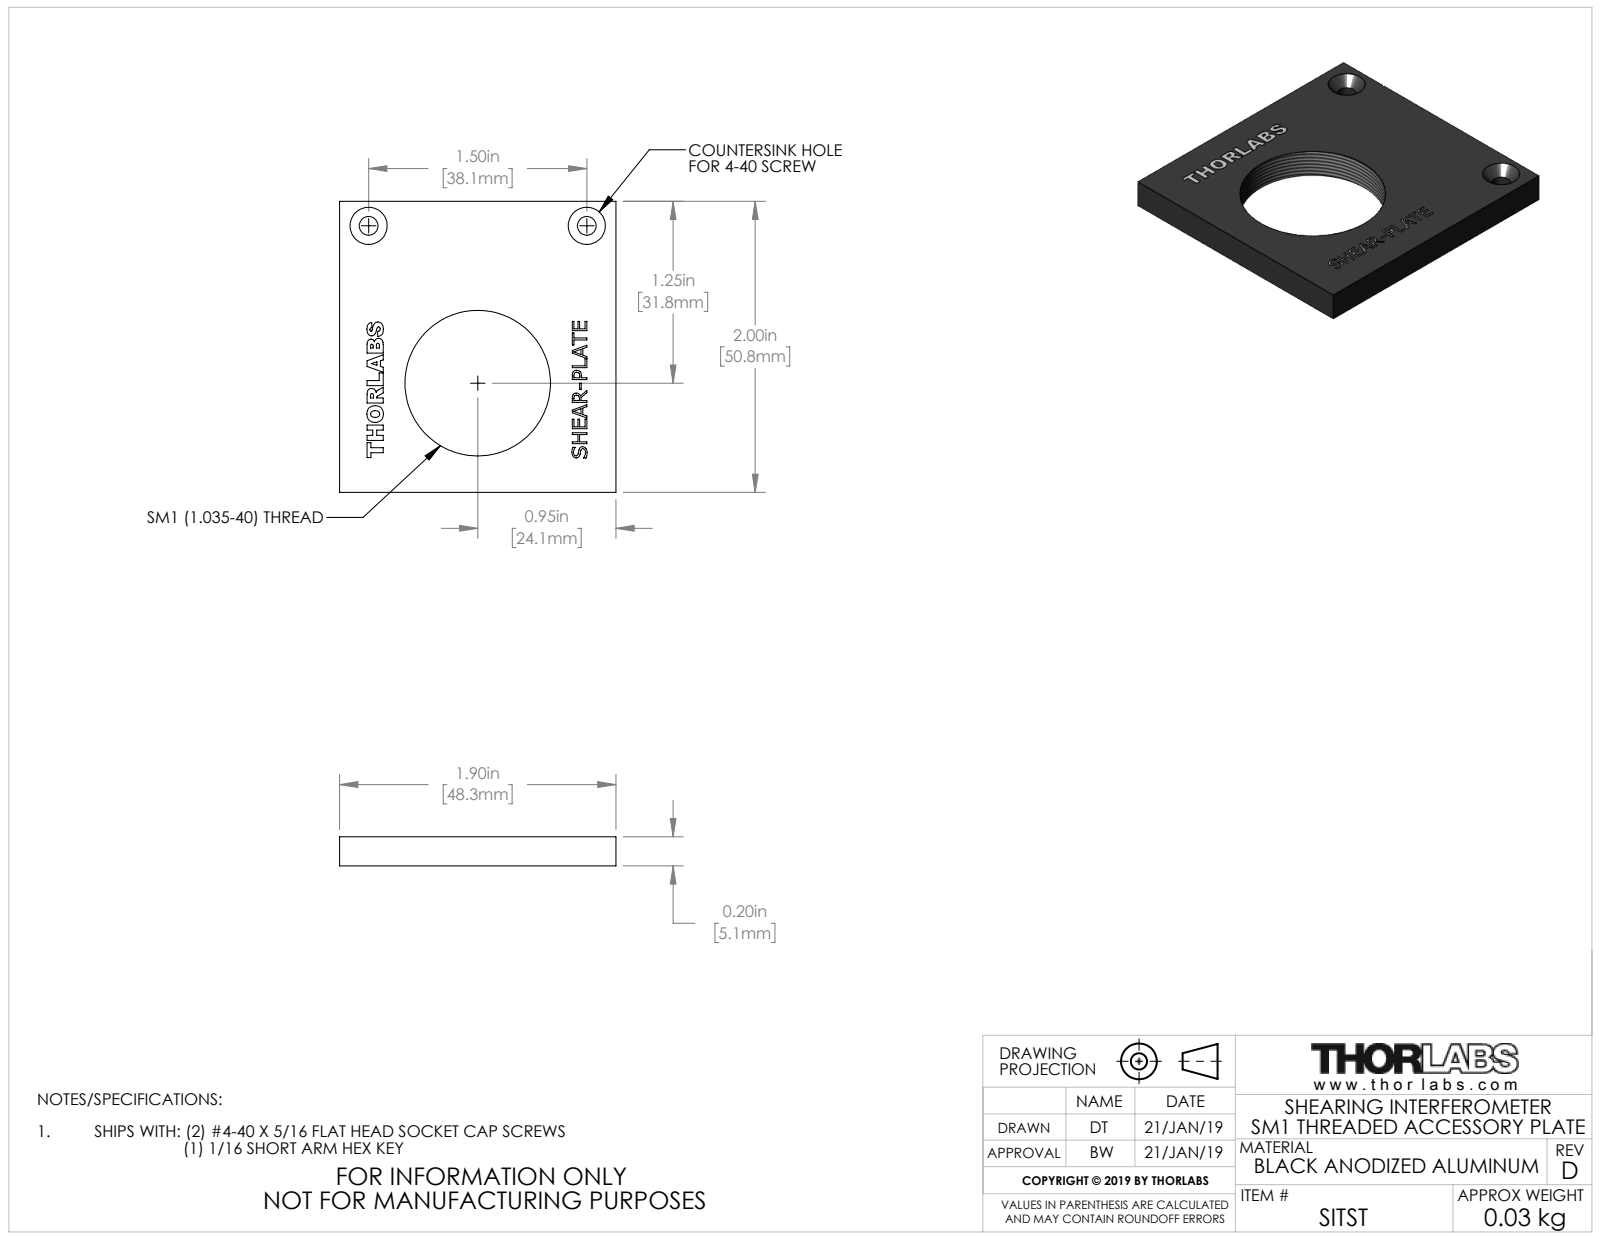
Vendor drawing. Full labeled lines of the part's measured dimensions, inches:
Part name (STEP PRODUCT): 18496-E0W
STEP written by: SolidWorks 2018 (CONFIG_CONTROL_DESIGN)
Units: inches
Bodies: 1 solid, 44 faces (34 planar, 6 cylindrical, 4 other)
Overall size (bounding box): 2 × 1.9 × 0.2
Volume: 0.595 in³ · Surface area: 8.308 in²
Round holes (diameter × count): ⌀0.129 ×2, ⌀1 ×1
Main face-to-face distances: 0.2, 1.9, 2
Hole centre spacings: 1.316, 1.5
